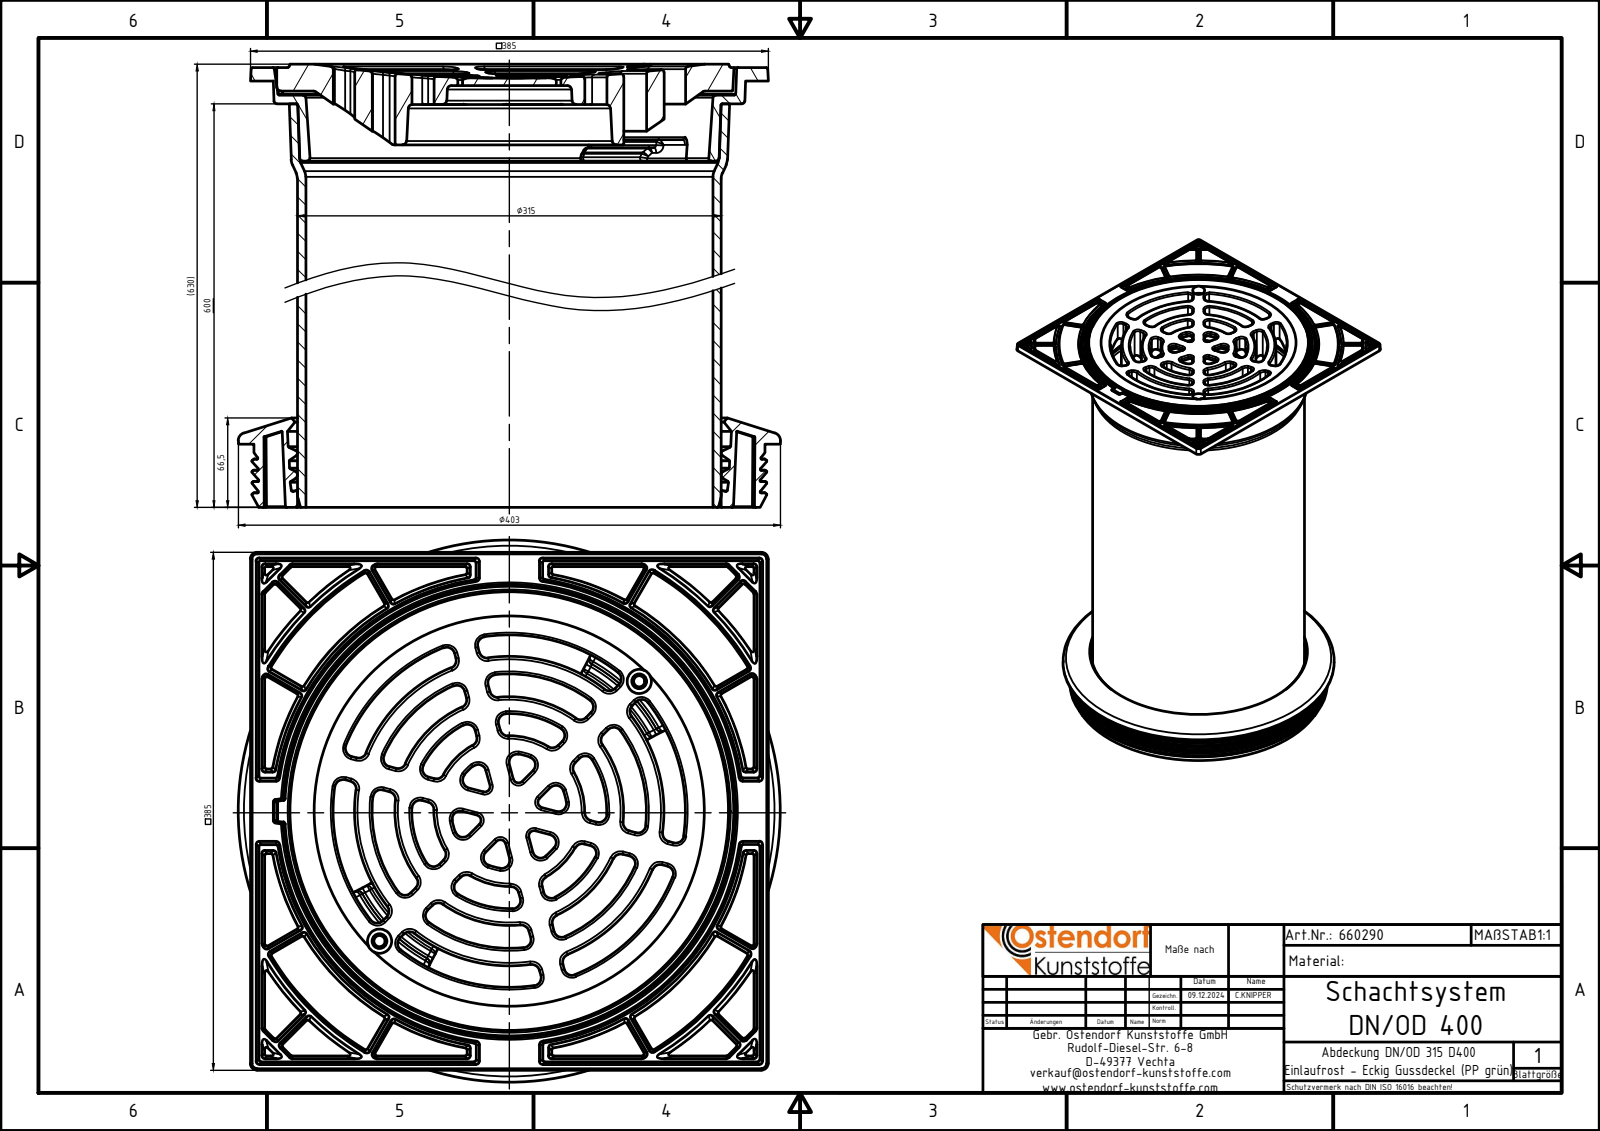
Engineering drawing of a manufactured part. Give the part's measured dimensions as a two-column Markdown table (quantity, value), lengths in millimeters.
| quantity | value |
| --- | --- |
| part name | 660290z; 660300z; 660500z; 990060z (+2 more) |
| STEP written by | Autodesk Inventor 2024 (AUTOMOTIVE_DESIGN) |
| units | millimeters |
| bodies | 4 solids, 1586 faces (235 planar, 431 cylindrical, 920 other) |
| overall size | 629.5 × 403 × 403 |
| volume | 7 698 000 mm³ |
| surface area | 2 173 000 mm² |
| round holes (diameter × count) | 8.38 × 2, 11 × 2, 18 × 2, 302.6 × 1, 315 × 1 |
| round bosses / shafts (diameter × count) | 403 × 1, 380 × 1 |
| partial cylindrical surfaces (radius × count) | 1 × 193, 6 × 84, 2.5 × 48, 4 × 14, 2 × 4, 3 × 1, 43 × 1, 56 × 1 |
| main face-to-face distances | 10, 7.5, 17.5, 2.5, 17, 27, 9.5, 29.5, 20, 12.5 |
| hole center spacings | 136.5, 273 |
